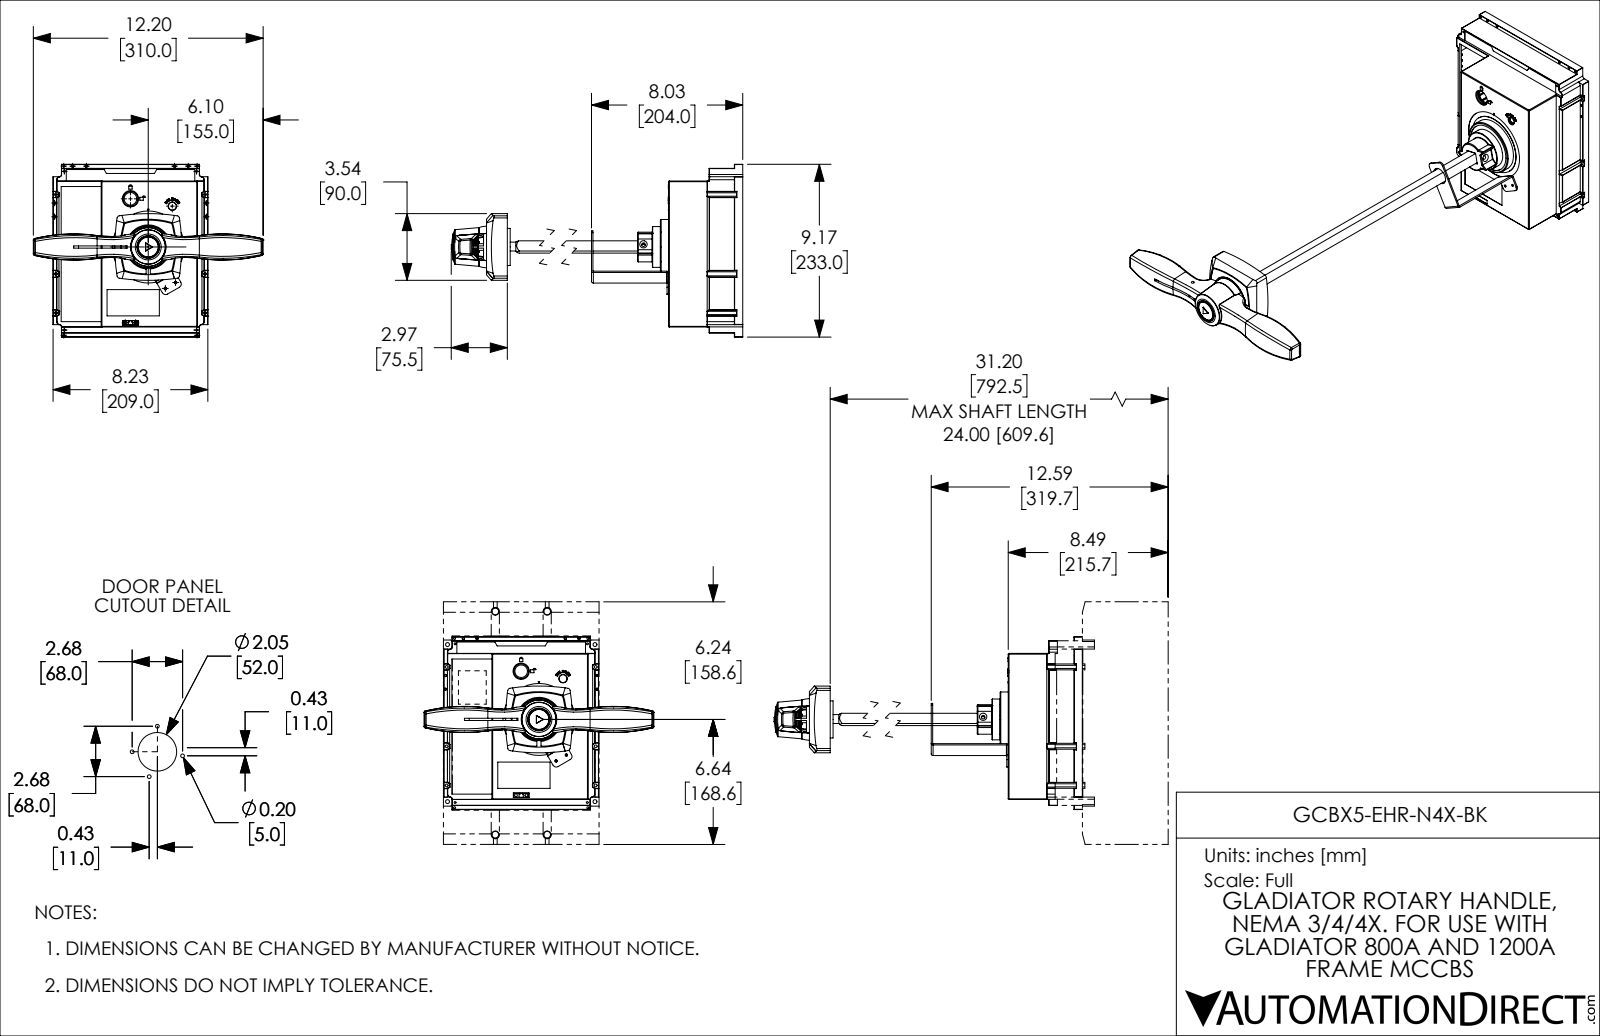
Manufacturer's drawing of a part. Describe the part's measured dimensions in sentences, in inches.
The part is named "GCBX5-EHR-N4X-BK". Its 3-D file was written by "SolidWorks 2021 (CONFIG_CONTROL_DESIGN)". It is 6 solids with 2788 faces: 1858 planar, 518 cylindrical and 412 other. Overall it measures 25.669 by 12.205 by 9.173 inches. Its volume is 53.3 cubic inches and its surface area 726.5 square inches. Round holes: 18 of diameter 0.102, 8 of diameter 0.15, 7 of diameter 0.197, 4 of diameter 0.315, 2 of diameter 0.118, 2 of diameter 0.126, 2 of diameter 0.169, 1 of diameter 0.157, 1 of diameter 0.28, 1 of diameter 0.394, 1 of diameter 0.413, 1 of diameter 0.669. Round bosses or shafts: 2 of diameter 0.236, 1 of diameter 3.268, 1 of diameter 2.913, 1 of diameter 2.874, 1 of diameter 2.343, 1 of diameter 2.205, 1 of diameter 2.165, 1 of diameter 1.969. Partial cylindrical surfaces (rounded edges, fillets, slot ends): 81 of radius 0.012, 56 of radius 0.02, 25 of radius 0.039, 14 of radius 0.079, 10 of radius 0.098, 8 of radius 0.118, 8 of radius 0.236, 6 of radius 0.146. The main face-to-face distances are 0.118, 0.315, 0.098, 7.362, 0.669, 7.638, 7.953, 0.354, 8.307, 0.552. The hole center spacings are 0.278, 0.728, 7.061, 8.701, 11.202, 7.804, 7.913, 0.458.
